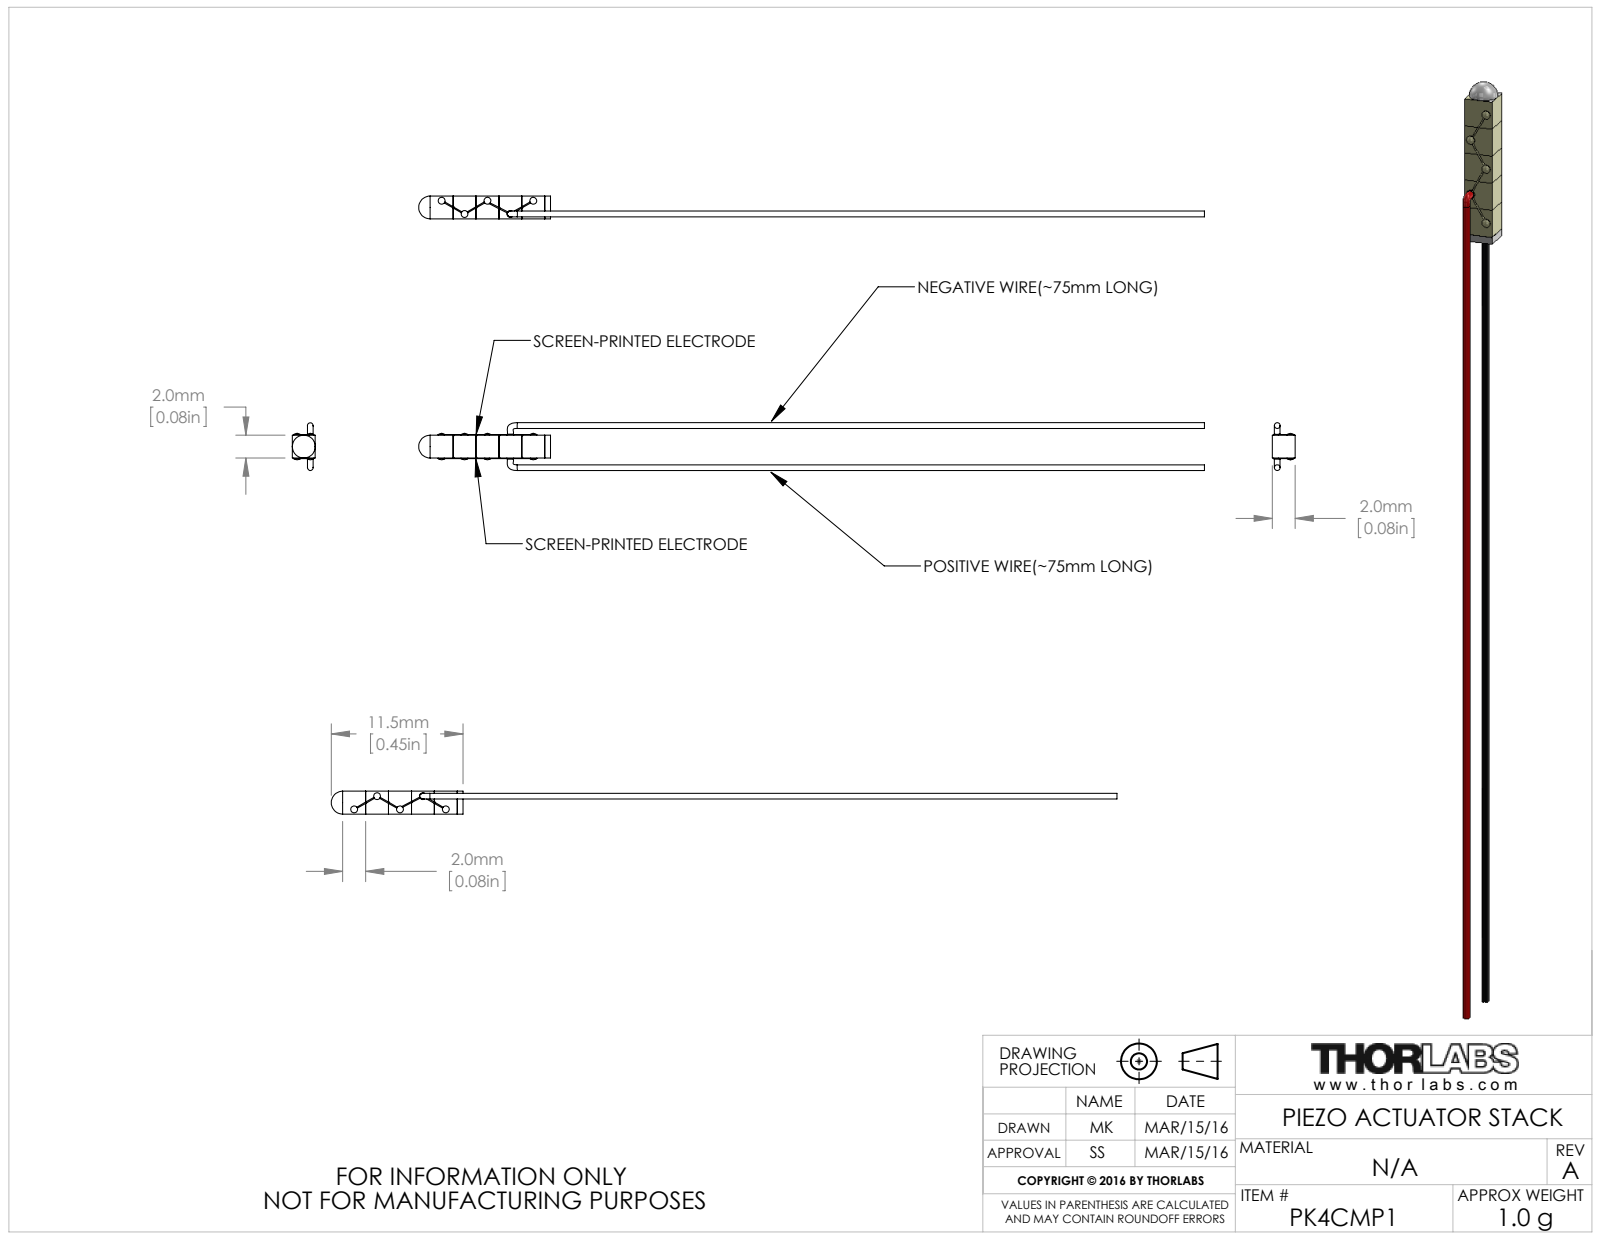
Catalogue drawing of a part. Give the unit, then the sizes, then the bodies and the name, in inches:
Units: inches
Overall size (bounding box): 2.701 × 0.165 × 0.079
Round bosses / shafts (diameter × count): ⌀0.024 ×5
Main face-to-face distances: 0.079, 0.157, 0.236, 0.315, 0.02, 0.099, 0.178, 0.256, 0.335, 0.079
Volume: 0.004 in³ · Surface area: 0.512 in²
Bodies: 2 solids, 123 faces (47 planar, 46 cylindrical, 30 other)
Part name (STEP PRODUCT): CTN003604
STEP written by: SolidWorks 2014 (AUTOMOTIVE_DESIGN)
